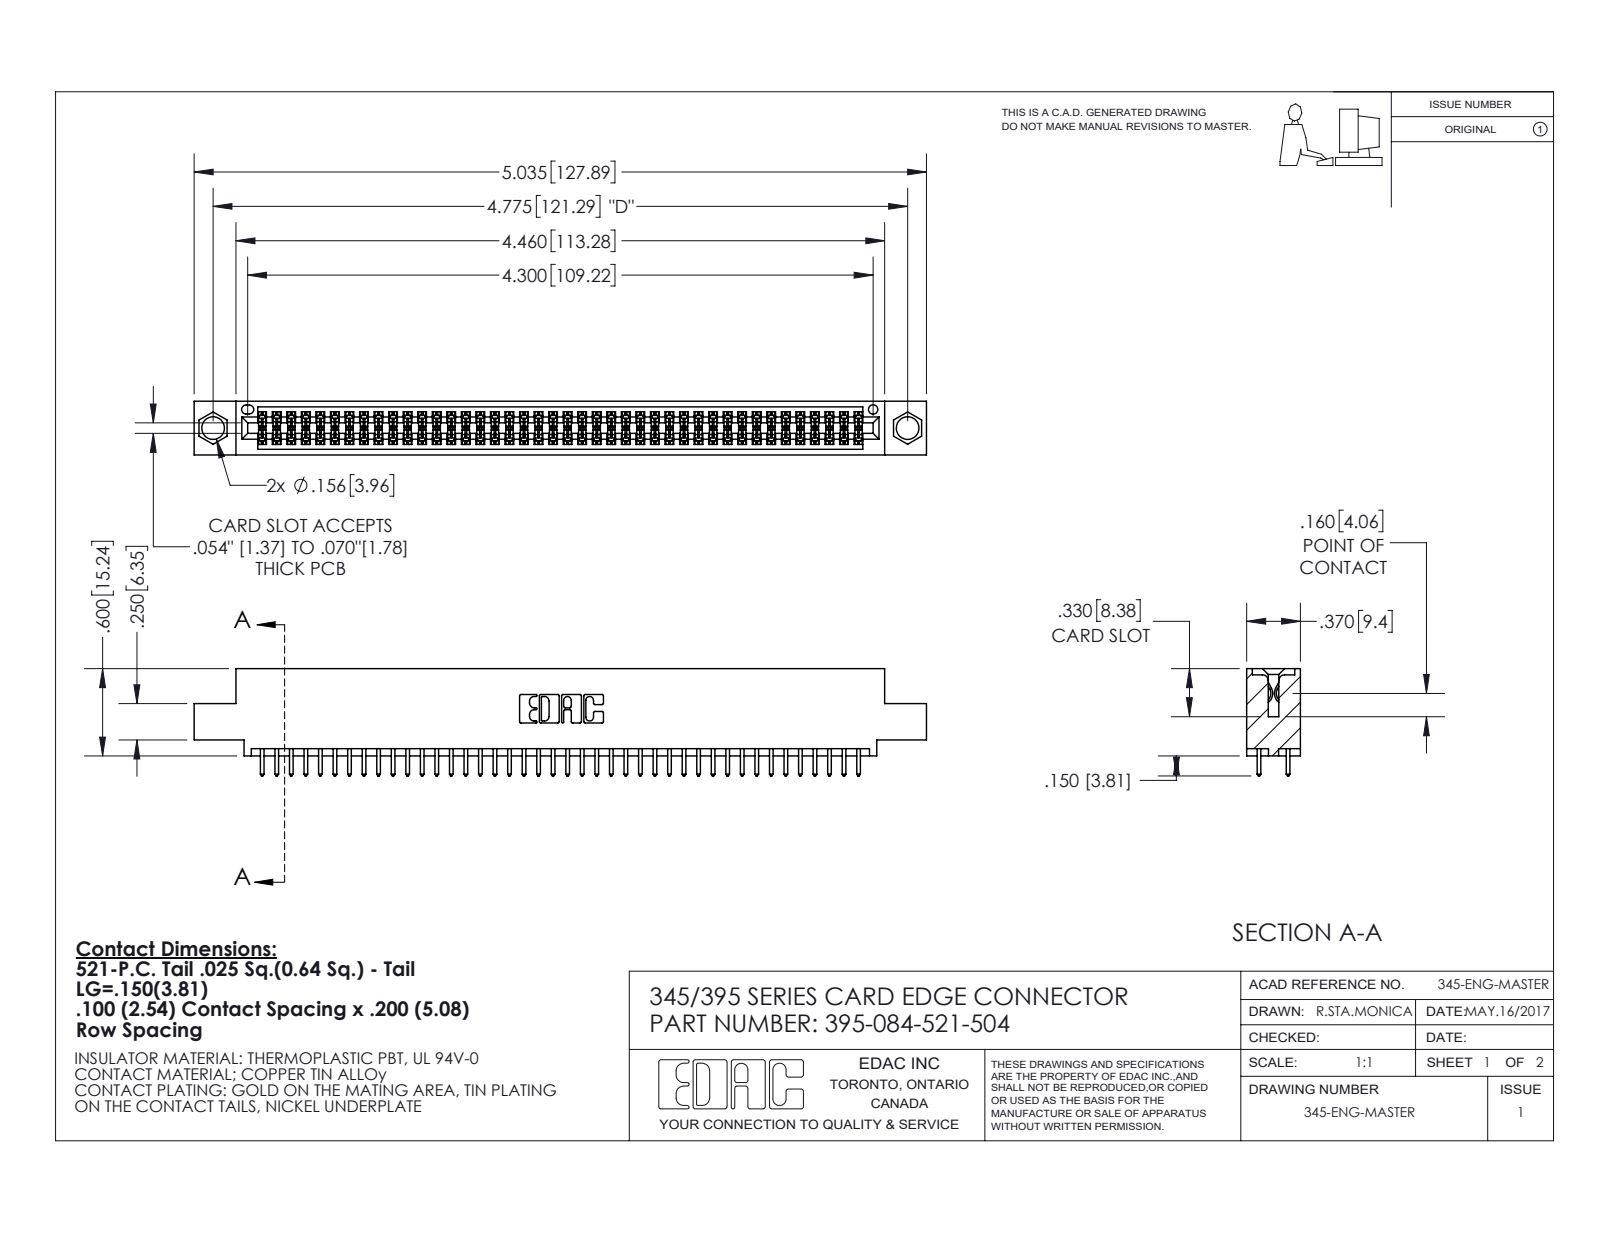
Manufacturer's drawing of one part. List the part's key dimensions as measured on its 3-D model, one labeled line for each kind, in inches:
Part name (STEP PRODUCT): 345-292-001_345-293-121; 395-084-521-504; 345 Part_0.110 Offset - 0.156 Dia-TI
STEP written by: SolidWorks 2020 (CONFIG_CONTROL_DESIGN)
Units: inches
Bodies: 85 solids, 4344 faces (2870 planar, 1474 cylindrical, 0 other)
Overall size (bounding box): 5.035 × 0.737 × 0.37
Volume: 0.745 in³ · Surface area: 27.54 in²
Round holes (diameter × count): ⌀0.156 ×2, ⌀0.064 ×1
Partial cylindrical surfaces — rounded edges, fillets, slot ends (radius × count): R0.006 ×168, R0.01 ×84, R0.01 ×22, R0.007 ×6, R0.031 ×6, R0.026 ×3, R0.014 ×2, R0.019 ×2
Main face-to-face distances: 0.072, 0.298, 0.2, 0.37, 0.098, 0.272, 0.025, 0.225, 0.175, 0.149
Hole centre spacings: 0.27, 4.539, 4.775
